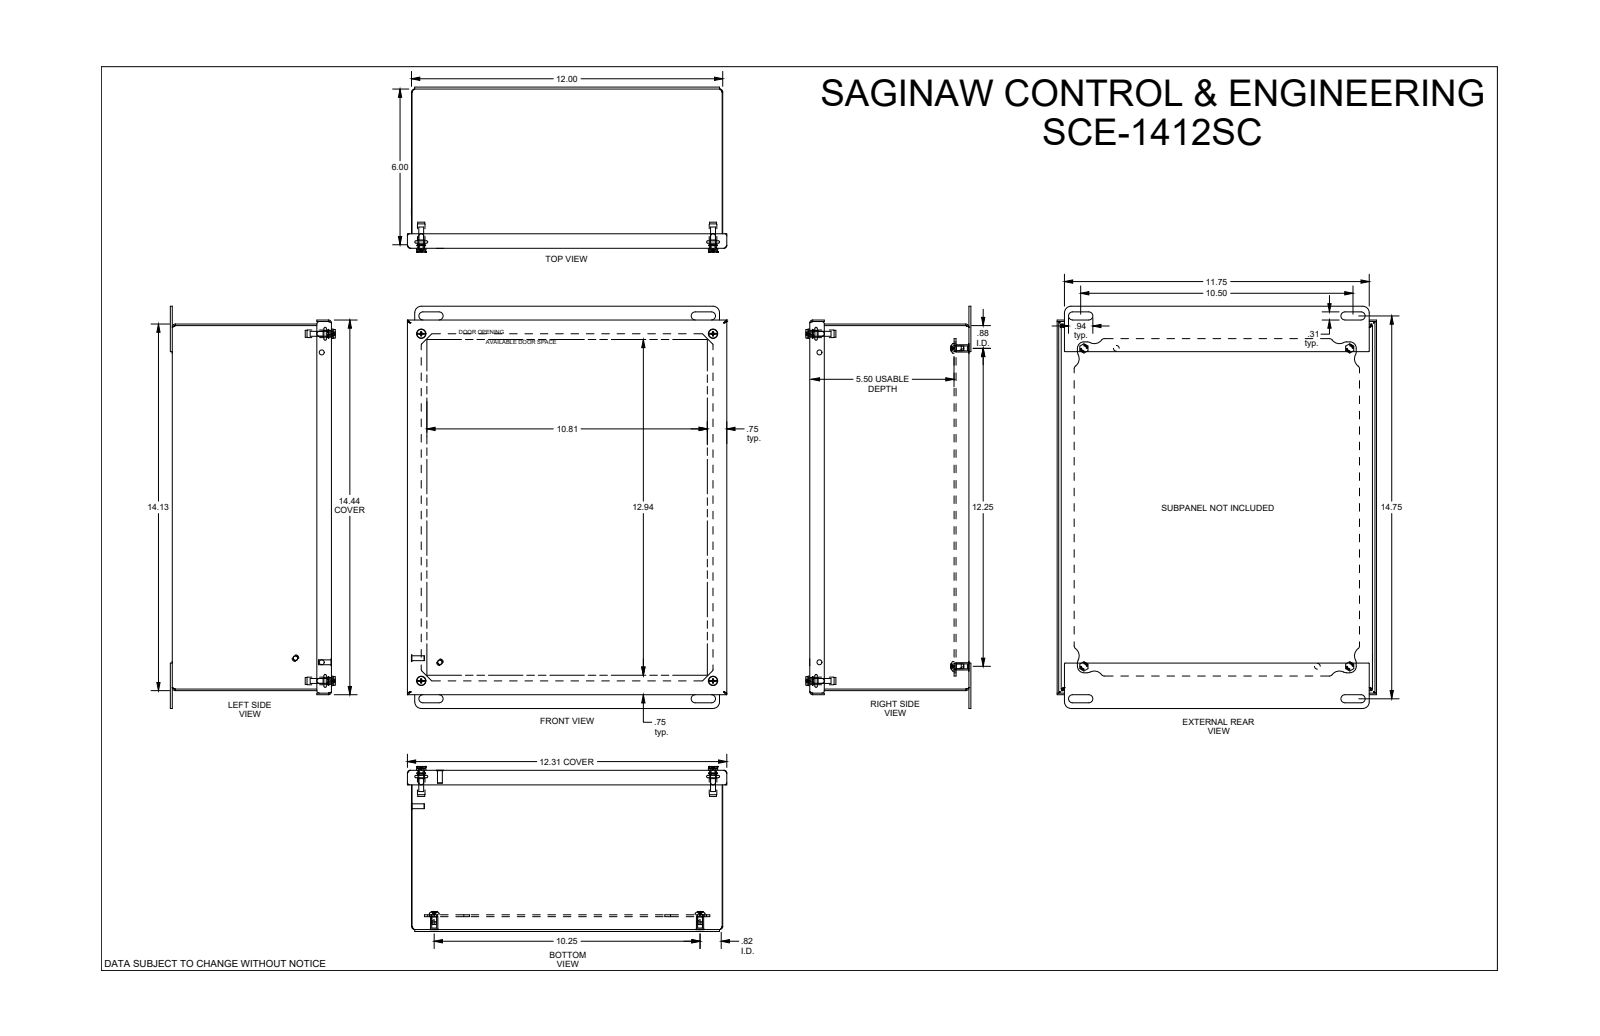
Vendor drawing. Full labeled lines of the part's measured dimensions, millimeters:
Part name (STEP PRODUCT): SCE-1412SC
STEP written by: SolidWorks 2019 (AUTOMOTIVE_DESIGN)
Units: millimetres
Bodies: 28 solids, 805 faces (328 planar, 207 cylindrical, 270 other)
Overall size (bounding box): 393.7 × 312.8 × 161.6
Volume: 934 700 mm³ · Surface area: 1 175 000 mm²
Round holes (diameter × count): ⌀4.8 ×8, ⌀6.4 ×8, ⌀5.6 ×4, ⌀6.8 ×4, ⌀7.1 ×4, ⌀8.1 ×4, ⌀4.7 ×2, ⌀5.5 ×2, ⌀4.9 ×1
Round bosses / shafts (diameter × count): ⌀4.8 ×10, ⌀11.1 ×4, ⌀9.5 ×4, ⌀9.2 ×4, ⌀8.6 ×4, ⌀8.5 ×4, ⌀7.4 ×4, ⌀7.1 ×4
Partial cylindrical surfaces — rounded edges, fillets, slot ends (radius × count): R3.2 ×16, R6.4 ×16, R1.5 ×12, R0.1 ×8, R1.3 ×8, R1.6 ×8, R4 ×8, R6.5 ×8
Main face-to-face distances: 1.5, 154.3, 155.8, 152.8, 303.3, 139.8, 1.9, 14.5, 13, 141.4
Hole centre spacings: 19.1, 273.4, 325.7, 424.8, 31.8, 46.7, 228.6, 241.7
